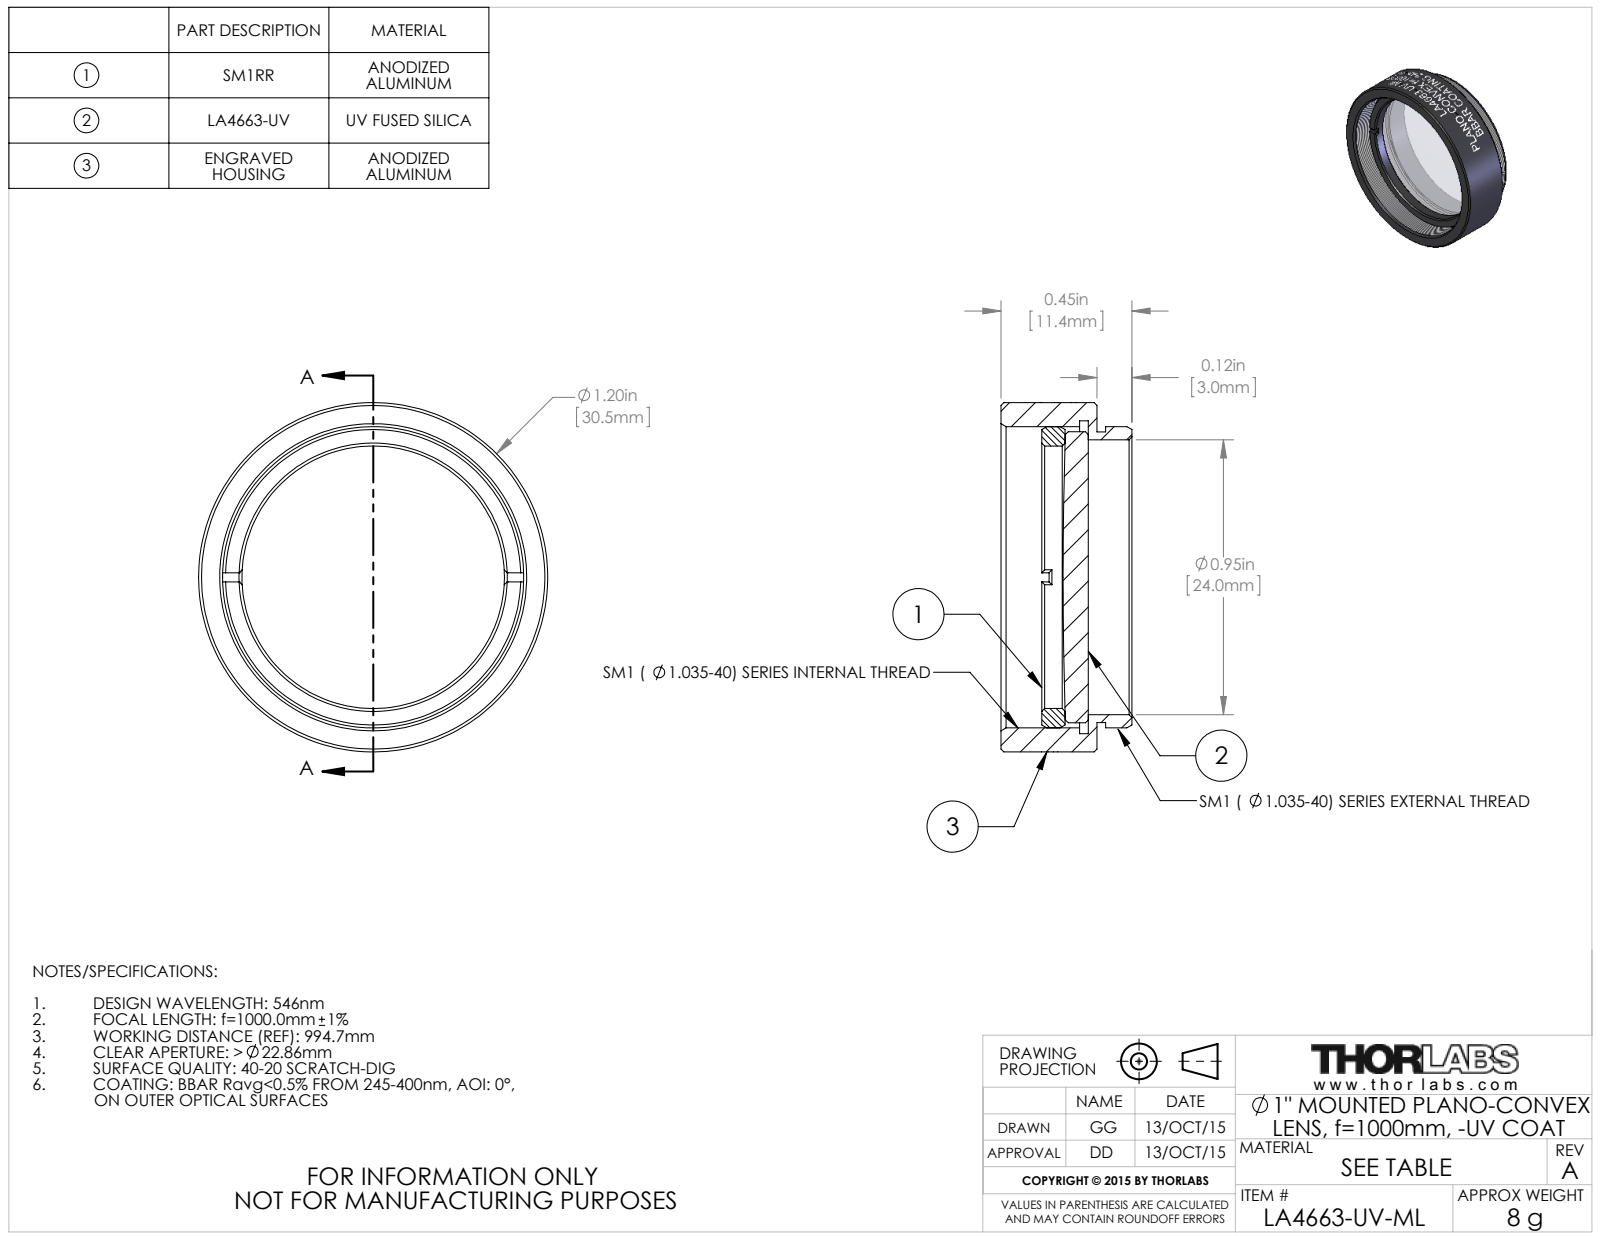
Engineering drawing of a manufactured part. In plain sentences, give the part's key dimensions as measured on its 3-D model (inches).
The part is named "TTN039351-E0W". Its 3-D file was written by "SolidWorks 2014 (CONFIG_CONTROL_DESIGN)". It is 3 solids with 163 faces: 20 planar, 115 cylindrical and 28 other. Overall it measures 1.2 by 1.2 by 0.45 inches. Its volume is 0.191 cubic inches and its surface area 6.648 square inches. Round holes: 1 of diameter 0.902, 1 of diameter 0.945, 1 of diameter 1.075. Round bosses or shafts: 1 of diameter 1.2, 1 of diameter 1.035, 1 of diameter 1, 1 of diameter 0.999. The main face-to-face distances are 0.03, 0.33, 0.3, 0.22, 0.14, 0.11, 0.08, 0.19, 0.16, 0.08.
